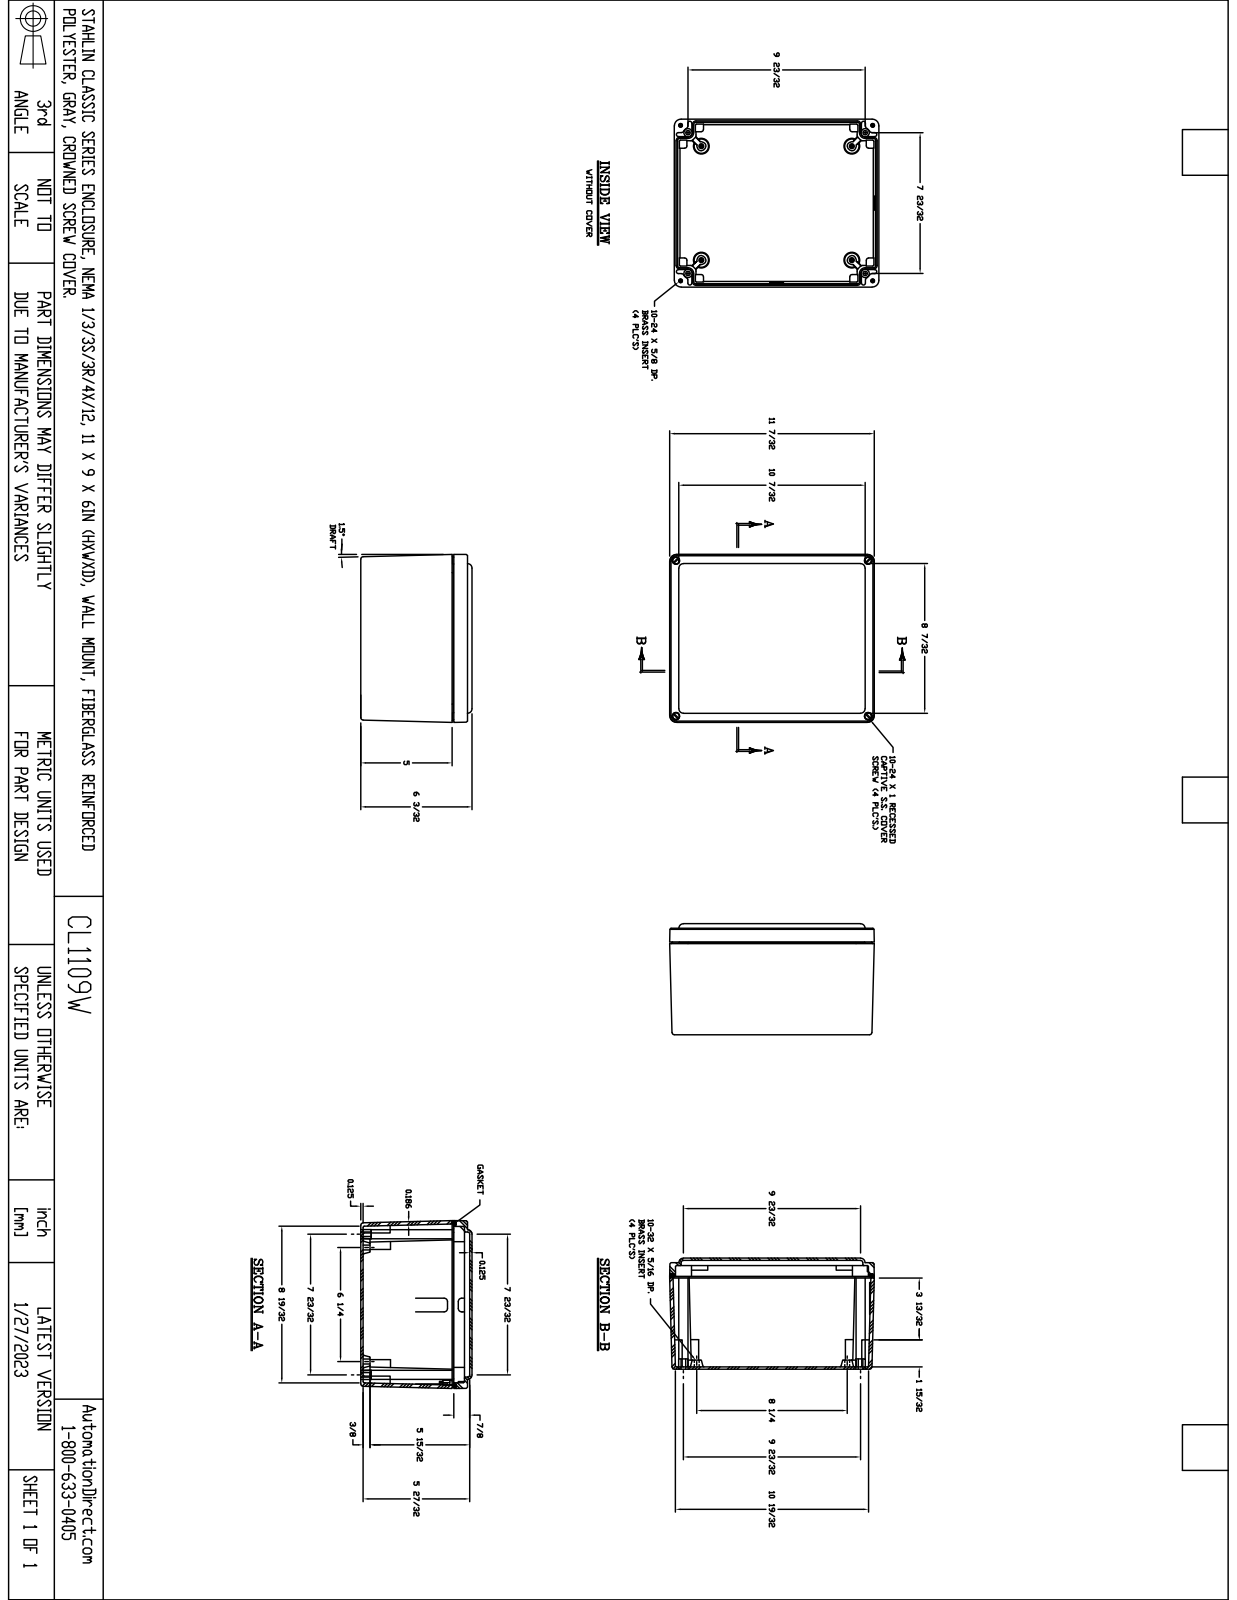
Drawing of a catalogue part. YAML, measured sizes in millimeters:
part_name: "CE1109W"
step_written_by: "SolidWorks 2018 (AUTOMOTIVE_DESIGN)"
units: millimeters
bodies: {solids: 23, faces: 1101, planar: 437, cylindrical: 296, other: 368}
overall_size: [285.3, 234.5, 154.8]
volume: 1366000
surface_area: 622800
round_holes:
  - {diameter: 7.1, count: 8}
  - {diameter: 4, count: 4}
  - {diameter: 4, count: 4}
  - {diameter: 4.8, count: 4}
  - {diameter: 5.6, count: 4}
  - {diameter: 5.8, count: 4}
  - {diameter: 7.1, count: 4}
  - {diameter: 8, count: 4}
  - {diameter: 10.3, count: 4}
  - {diameter: 13.5, count: 4}
  - {diameter: 3.7, count: 3}
  - {diameter: 3.7, count: 1}
round_bosses_or_shafts:
  - {diameter: 9.5, count: 4}
  - {diameter: 9.2, count: 4}
  - {diameter: 4.9, count: 4}
partial_cylinders:
  - {radius: 0.8, count: 57}
  - {radius: 3.2, count: 38}
  - {radius: 1.6, count: 19}
  - {radius: 0.3, count: 16}
  - {radius: 1.6, count: 10}
  - {radius: 1.5, count: 8}
  - {radius: 4.8, count: 8}
  - {radius: 6.4, count: 8}
face_to_face_distances: [4.7, 3.2, 148.4, 154.8, 151.6, 3.2, 151.6, 129.4, 19.1, 6.4]
hole_center_spacings: [14.4, 14.6, 26.4, 40.8, 41, 178.7, 190.1, 190.2]
